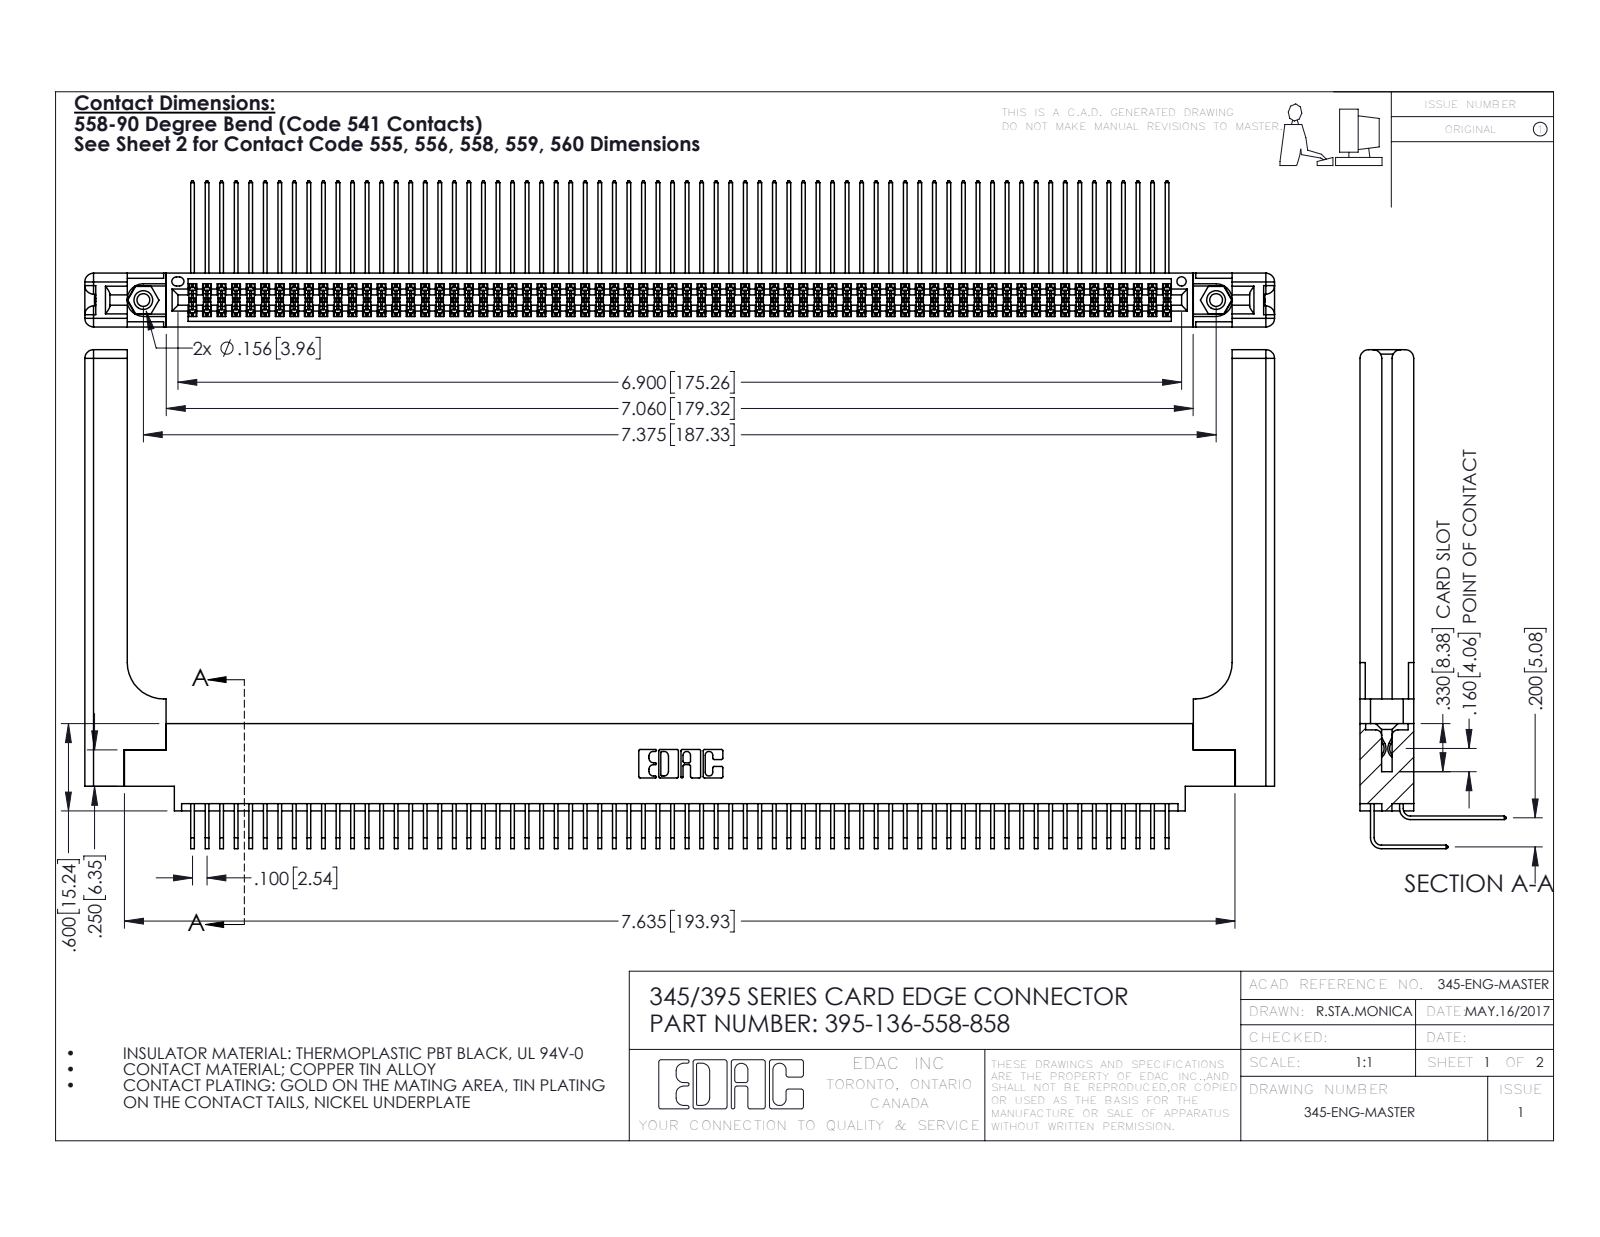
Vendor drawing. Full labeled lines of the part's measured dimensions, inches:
Part name (STEP PRODUCT): 345 Part_0.170 Offset - 0.156 Dia-TH; 345-292-001_558 559 Tail - 1; 345-220-058_345-220-058; 345-250-001_345-250-001-102 (+2 more)
STEP written by: SolidWorks 2016 (CONFIG_CONTROL_DESIGN)
Units: inches
Bodies: 141 solids, 7458 faces (4992 planar, 2406 cylindrical, 60 other)
Overall size (bounding box): 8.179 × 3.429 × 1.005
Volume: 1.804 in³ · Surface area: 62.89 in²
Round holes (diameter × count): ⌀0.089 ×2, ⌀0.125 ×2, ⌀0.156 ×2, ⌀0.064 ×1
Round bosses / shafts (diameter × count): ⌀0.155 ×2
Partial cylindrical surfaces — rounded edges, fillets, slot ends (radius × count): R0.006 ×271, R0.01 ×22, R0.06 ×16, R0.007 ×6, R0.031 ×6, R0.026 ×3, R0.014 ×2, R0.019 ×2
Main face-to-face distances: 0.072, 0.298, 0.37, 0.2, 0.098, 0.272, 0.025, 0.225, 0.175, 0.025
Hole centre spacings: 0.27, 7.139, 7.375
